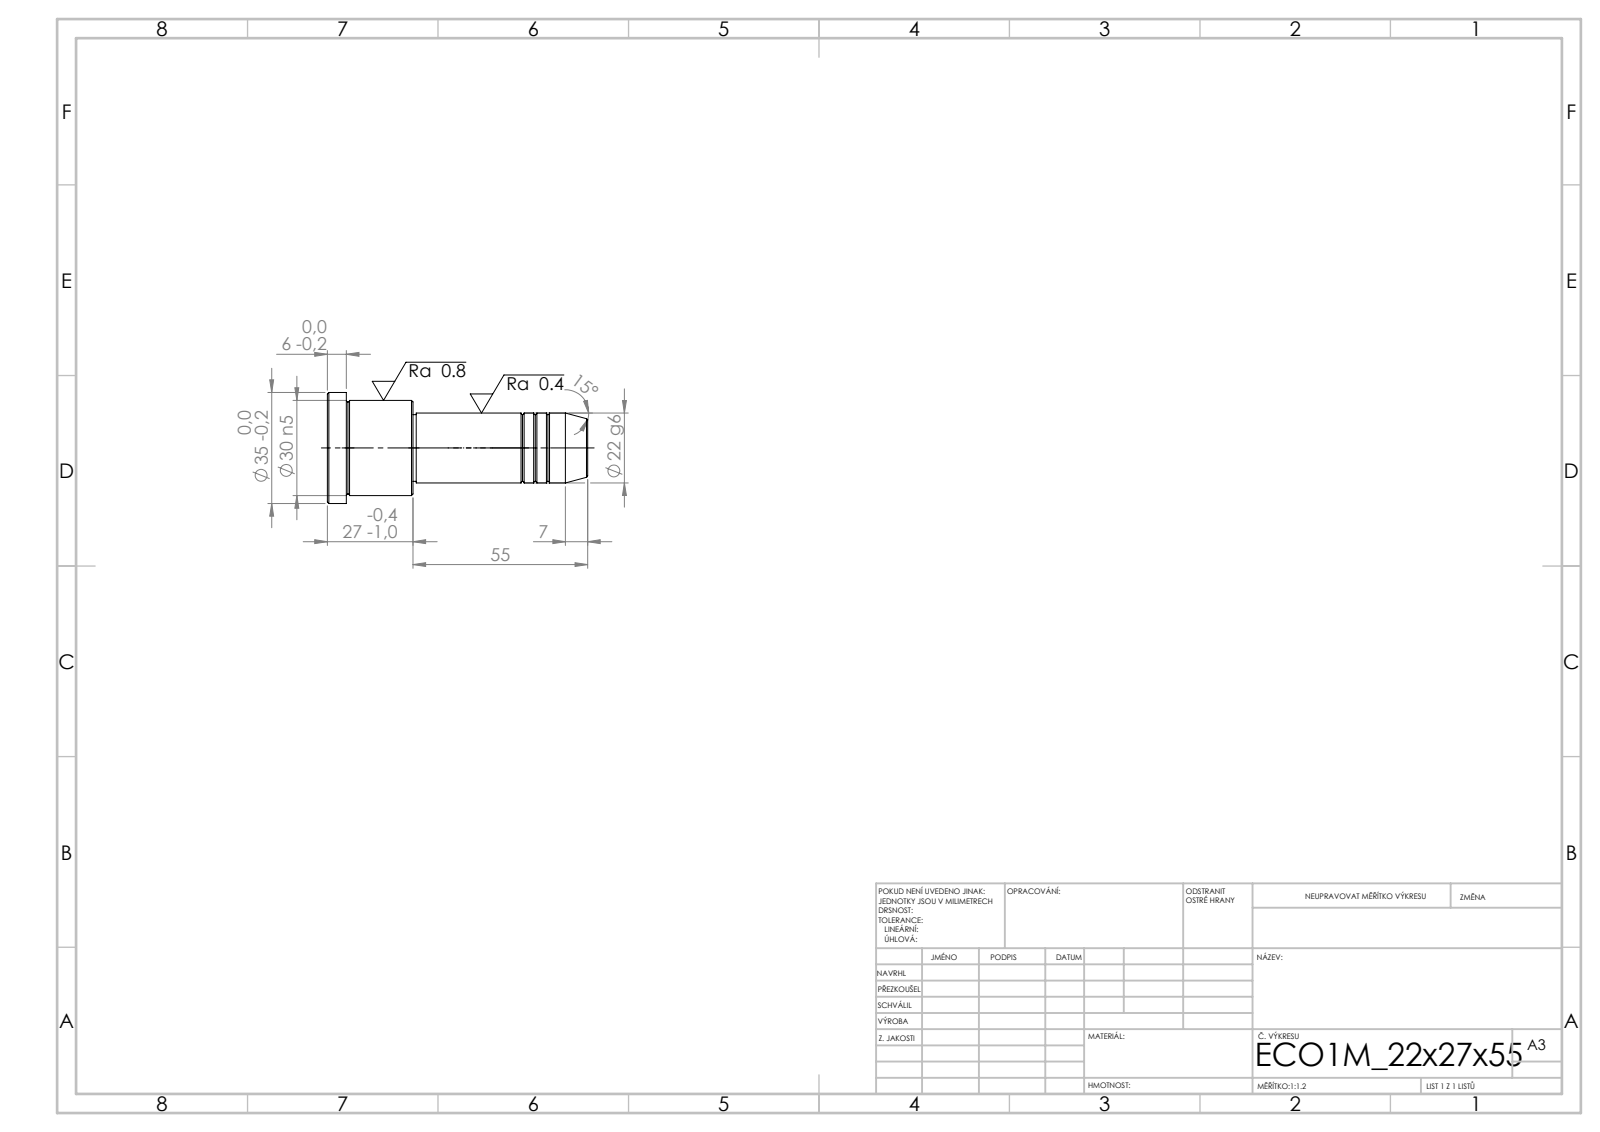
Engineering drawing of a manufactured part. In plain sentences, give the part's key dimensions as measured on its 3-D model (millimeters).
Its 3-D file was written by "SolidWorks 2019 (CONFIG_CONTROL_DESIGN)". It is 1 solid with 43 faces: 5 planar, 14 cylindrical and 24 other. Overall it measures 82 by 35 by 35 millimeters. Its volume is 40 919 cubic millimeters and its surface area 8 377 square millimeters. Round bosses or shafts: 1 of diameter 35, 1 of diameter 30, 1 of diameter 22, 1 of diameter 21. The main face-to-face distances are 27, 21, 6, 55, 76, 82, 54, 1, 22, 28.
